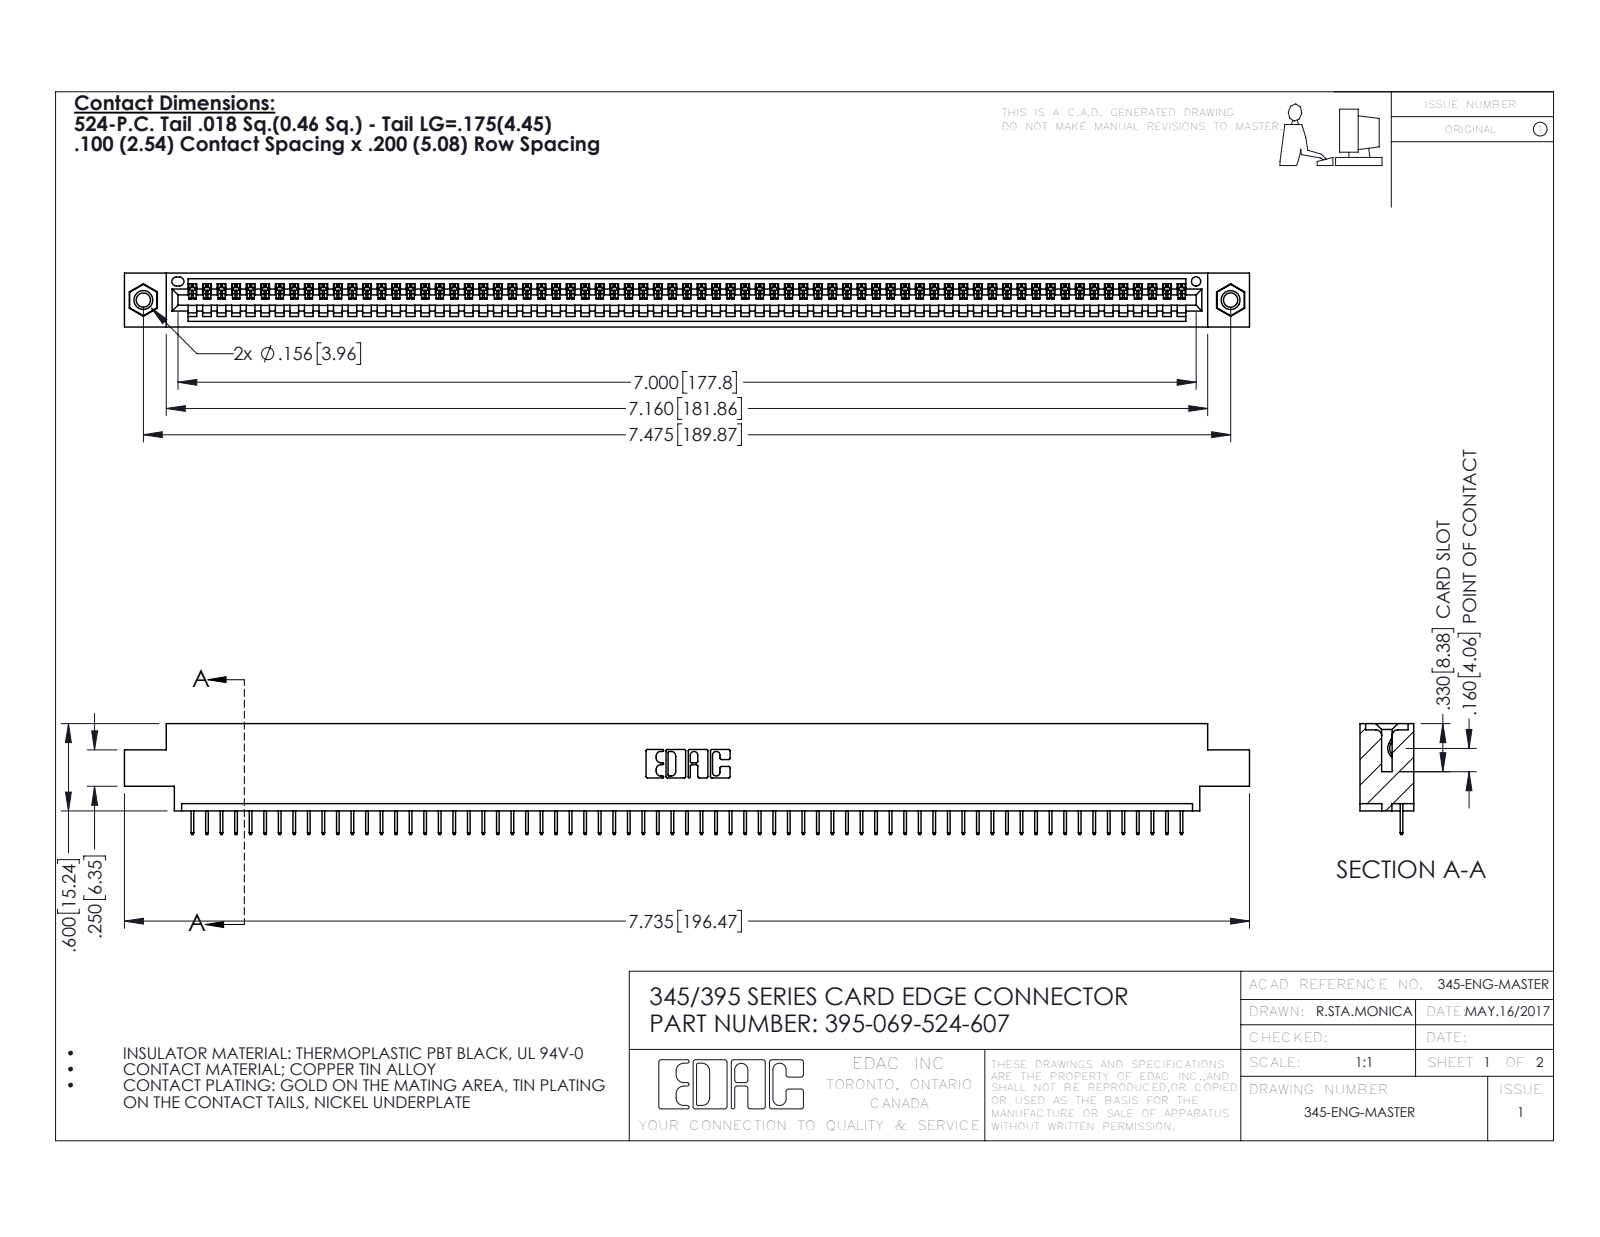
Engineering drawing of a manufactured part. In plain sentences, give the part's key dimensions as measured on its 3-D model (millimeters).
The part is named "345 Part_0.170 Offset - 0.156 Dia-TI; 345-250-001_345-250-005-103; 345-292-001_345-293-124; 395-069-524-607". Its 3-D file was written by "SolidWorks 2016 (CONFIG_CONTROL_DESIGN)". It is 72 solids with 4468 faces: 3290 planar, 1162 cylindrical and 16 other. Overall it measures 196.5 by 19.4 by 9.4 millimeters. Its volume is 18 480 cubic millimeters and its surface area 24 220 square millimeters. Round holes: 2 of diameter 2.5, 2 of diameter 3.2, 2 of diameter 4, 1 of diameter 1.6. Round bosses or shafts: 2 of diameter 3.9. Partial cylindrical surfaces (rounded edges, fillets, slot ends): 138 of radius 0.2, 22 of radius 0.3, 6 of radius 0.2, 6 of radius 0.8, 3 of radius 0.7, 2 of radius 0.8, 2 of radius 1, 1 of radius 0.4. The main face-to-face distances are 1.8, 7.6, 9.4, 5.1, 2.5, 6.9, 0.6, 5.7, 1.8, 4.4. The hole center spacings are 6.9, 183.9, 189.9.
